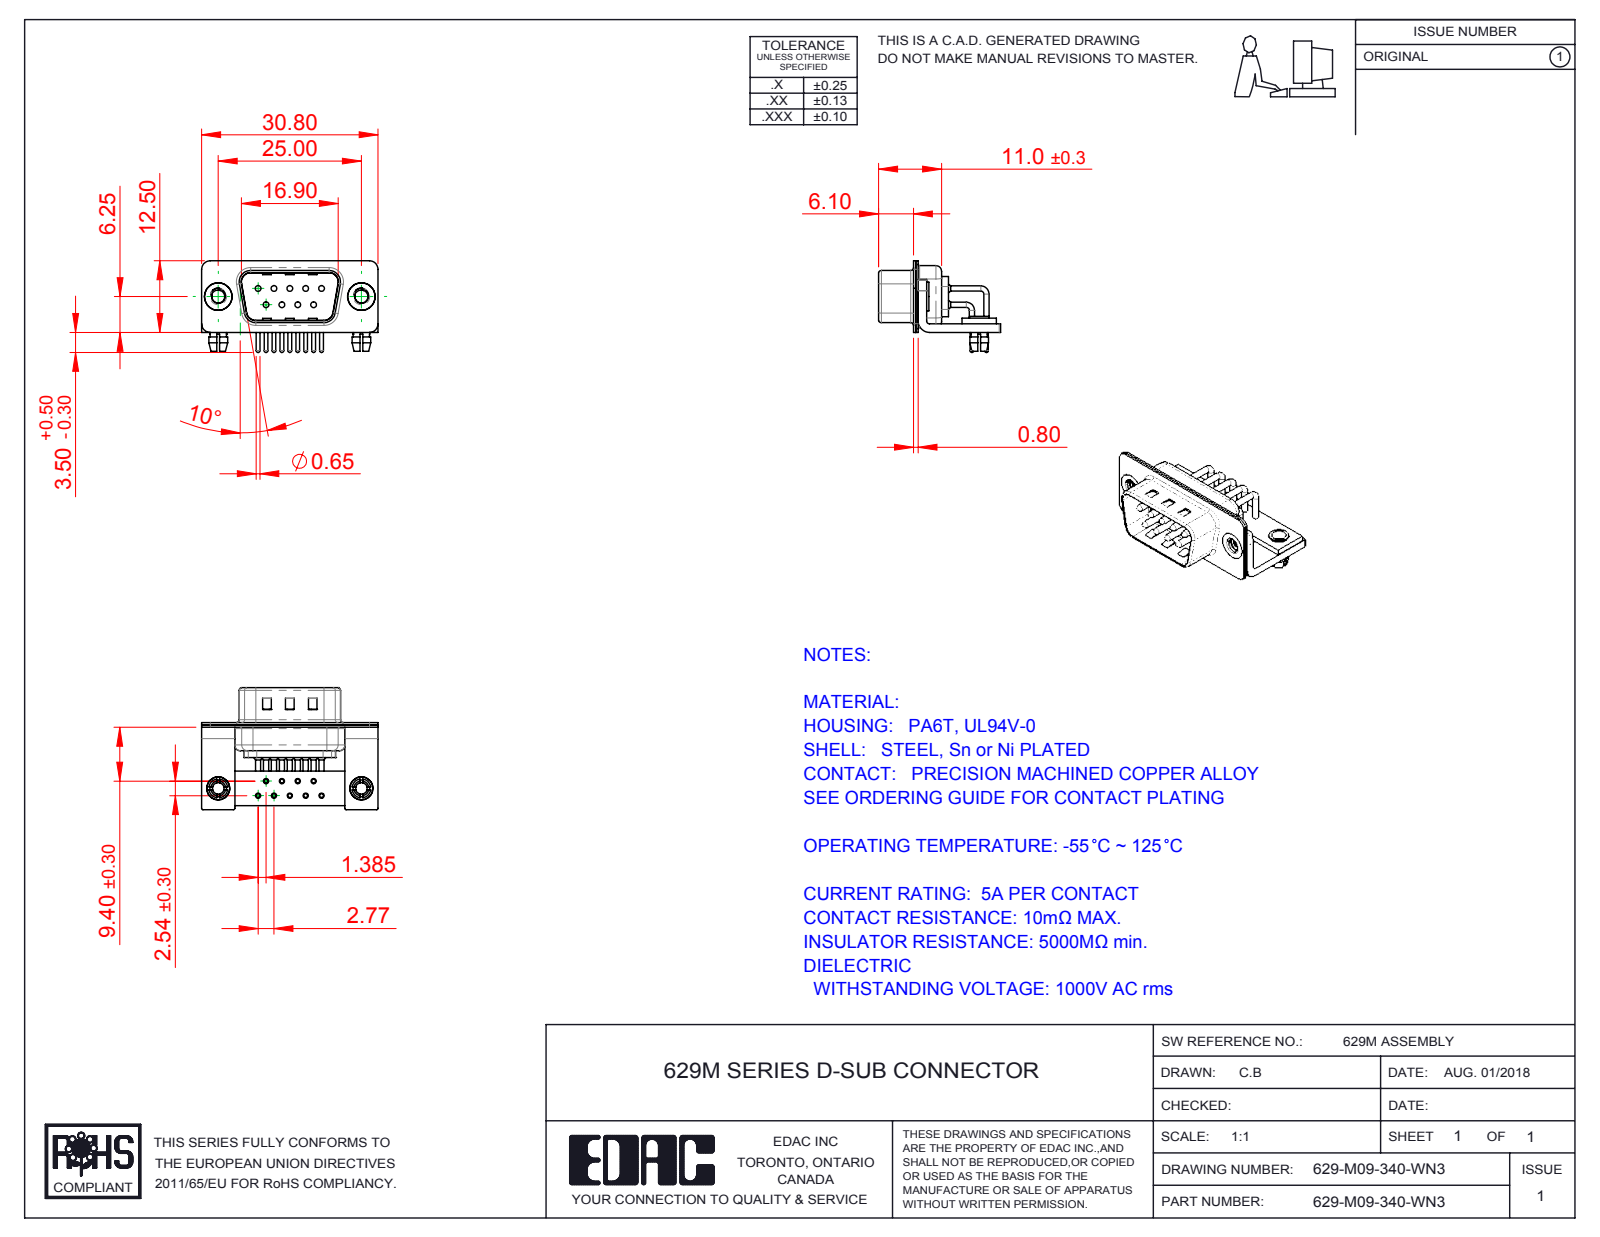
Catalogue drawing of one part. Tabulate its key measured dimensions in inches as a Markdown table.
| quantity | value |
| --- | --- |
| part name | 629M Contact Row 1; 629M Shell Rear_09 Contacts; 629M Shell Front_09 Contacts; 629M Housing_09 Contacts (+6 more) |
| STEP written by | SolidWorks 2016 (CONFIG_CONTROL_DESIGN) |
| units | inches |
| bodies | 19 solids, 1454 faces (757 planar, 525 cylindrical, 172 other) |
| overall size | 1.213 × 0.839 × 0.63 |
| volume | 0.113 in³ |
| surface area | 8.035 in² |
| round holes (diameter × count) | 0.079 × 11, 0.035 × 9, 0.039 × 9, 0.067 × 9, 0.089 × 2, 0.098 × 2, 0.126 × 2, 0.157 × 2, 0.189 × 2 |
| round bosses / shafts (diameter × count) | 0.059 × 9, 0.035 × 9, 0.026 × 9, 0.197 × 2, 0.193 × 2, 0.157 × 2, 0.134 × 2, 0.13 × 2 |
| partial cylindrical surfaces (radius × count) | 0.01 × 16, 0.059 × 16, 0.079 × 13, 0.02 × 9, 0.04 × 9, 0.063 × 8, 0.024 × 4, 0.026 × 4 |
| main face-to-face distances | 0.016, 0.059, 0.031, 0.033, 0.049, 0.075, 0.039, 0.098, 0.409, 0.376 |
| hole center spacings | 0.109, 0.218, 0.124, 0.192, 0.327, 0.114, 0.114, 0.198 |
